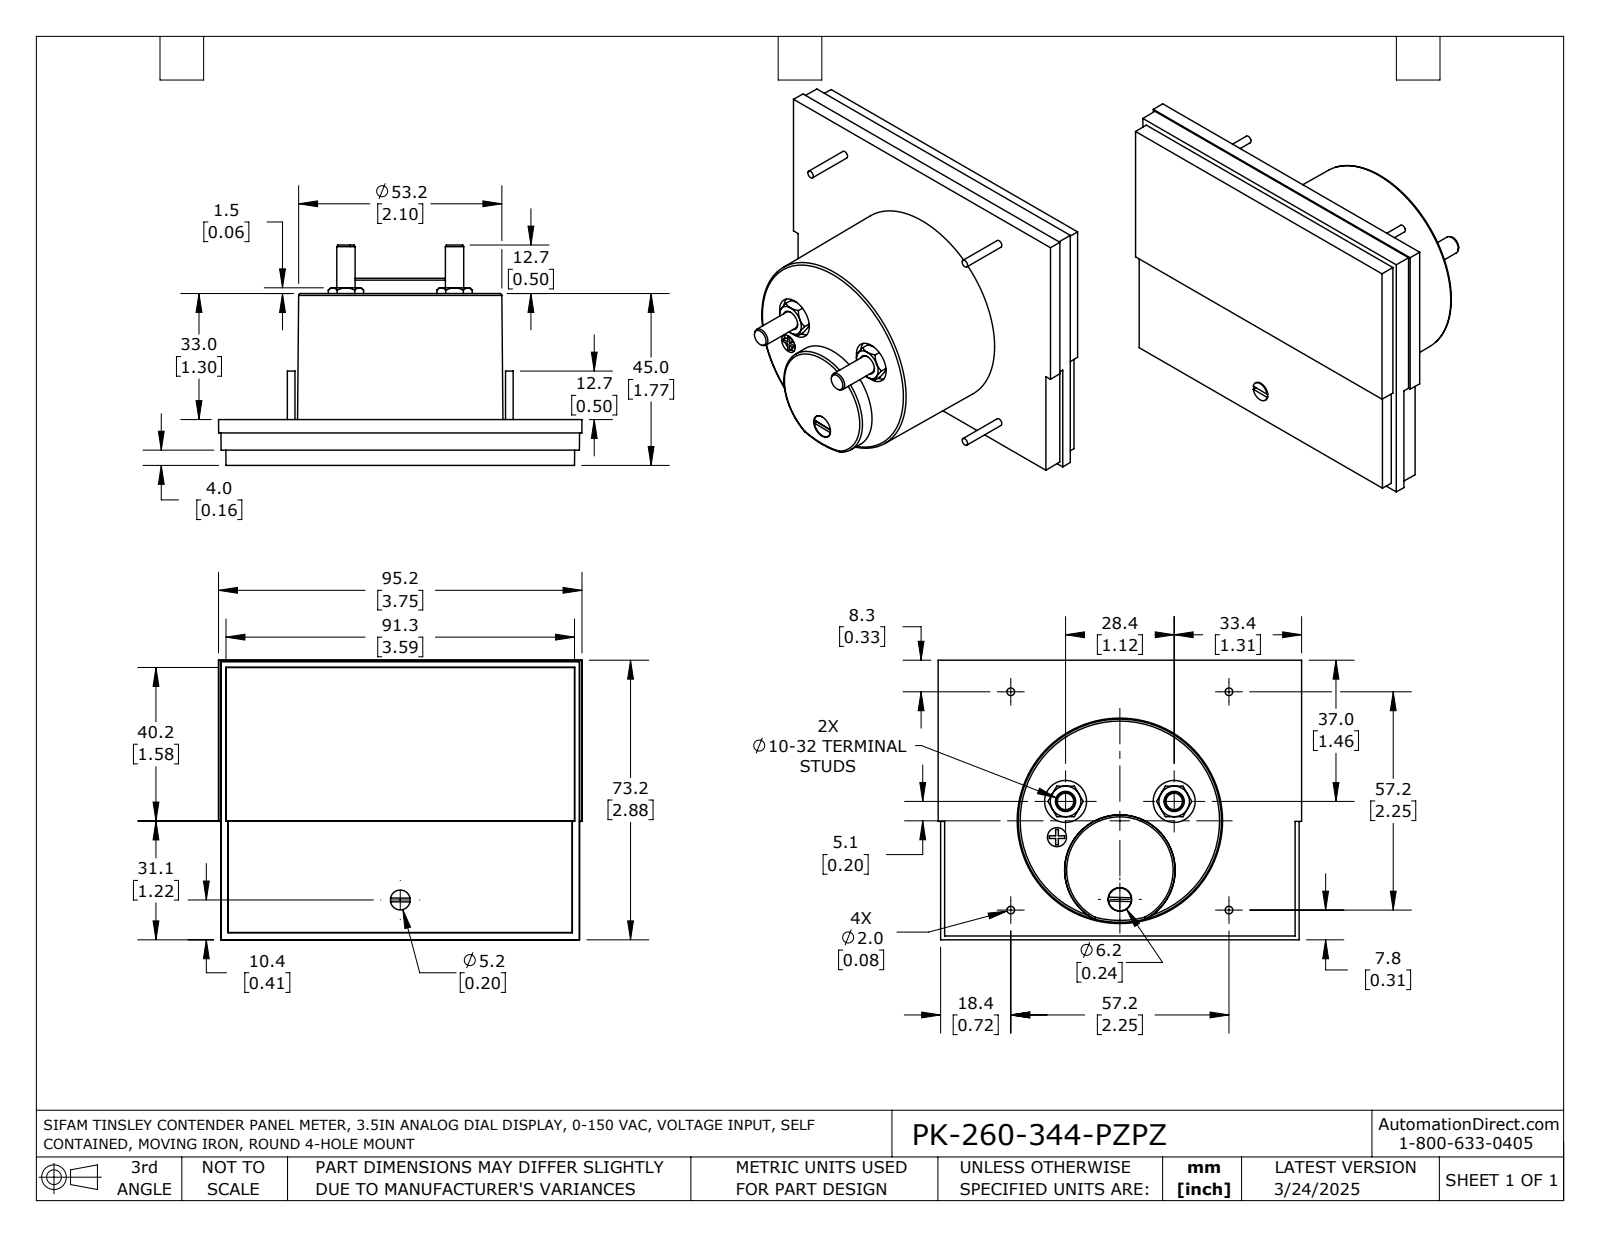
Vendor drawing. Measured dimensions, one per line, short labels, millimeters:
name: PK-260-344-PZPZ
written by: SolidWorks 2021 (AUTOMOTIVE_DESIGN)
unit: mm
bodies: 1 solid, 163 faces (76 planar, 31 cylindrical, 56 other)
size: 95.2 × 73.2 × 57.7
volume: 154 800 mm³; area: 24 770 mm²
holes: 2× ⌀11, 1× ⌀5, 1× ⌀6.2
bosses: 4× ⌀2, 2× ⌀4.8, 1× ⌀6, 1× ⌀5.2
rounds: 1× R2.5
face distances: 12, 0.8, 11.3, 45, 33, 44.2, 4, 1.9, 8, 37
hole spacings: 29.3, 9.6, 23.2, 28.4, 32.1
